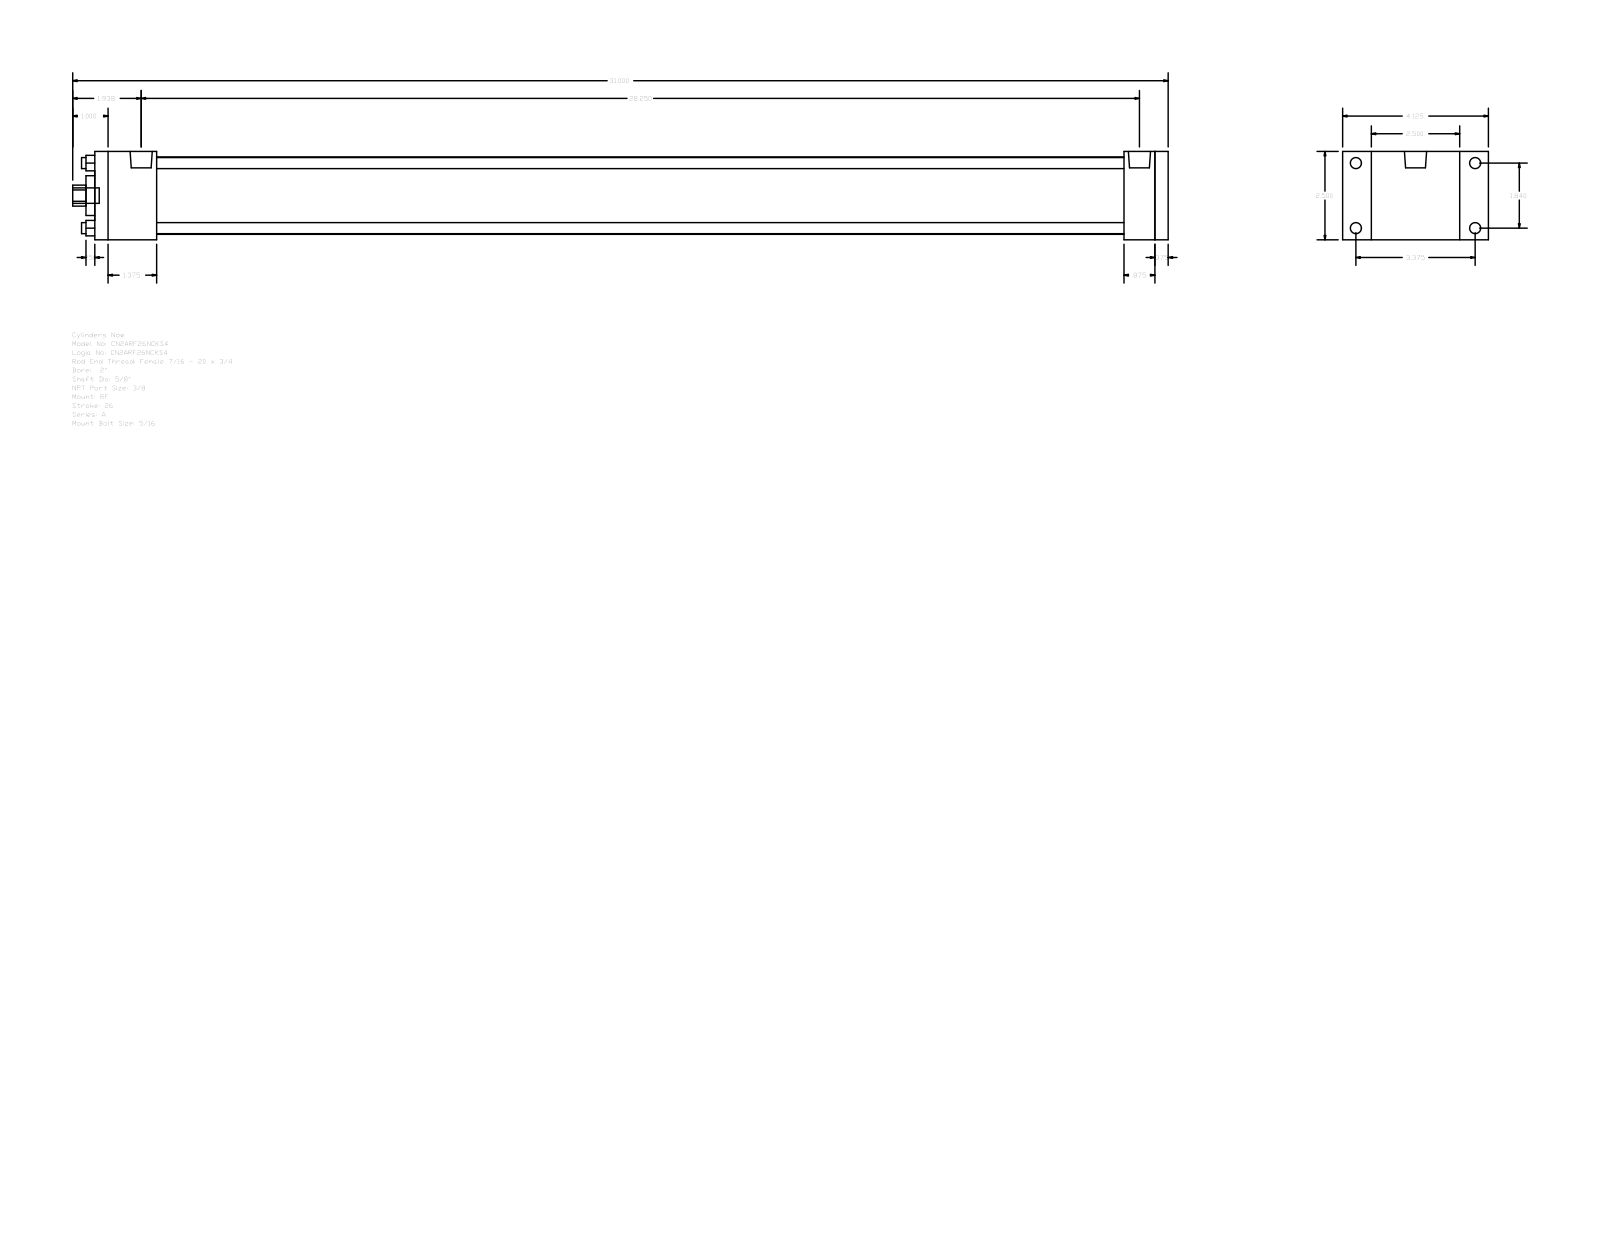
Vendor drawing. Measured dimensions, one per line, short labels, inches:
name: A_RF__0200_0.625
written by: GSSL Pune (CONFIG_CONTROL_DESIGN)
unit: in
bodies: 0 solids, 92 faces (64 planar, 28 cylindrical, 0 other)
size: 31 × 4.125 × 2.5
holes: 4× ⌀0.313, 1× ⌀0.625, 1× ⌀1.125, 1× ⌀2.19
bosses: 4× ⌀0.313, 4× ⌀0.219, 2× ⌀0.627, 1× ⌀0.437
rounds: 1× R0.297
face distances: 2.5, 30.375, 0.375, 30, 1.75, 28.25, 28.625, 29.125, 27.375, 0.875
hole spacings: 1.301, 1.84, 2.602
